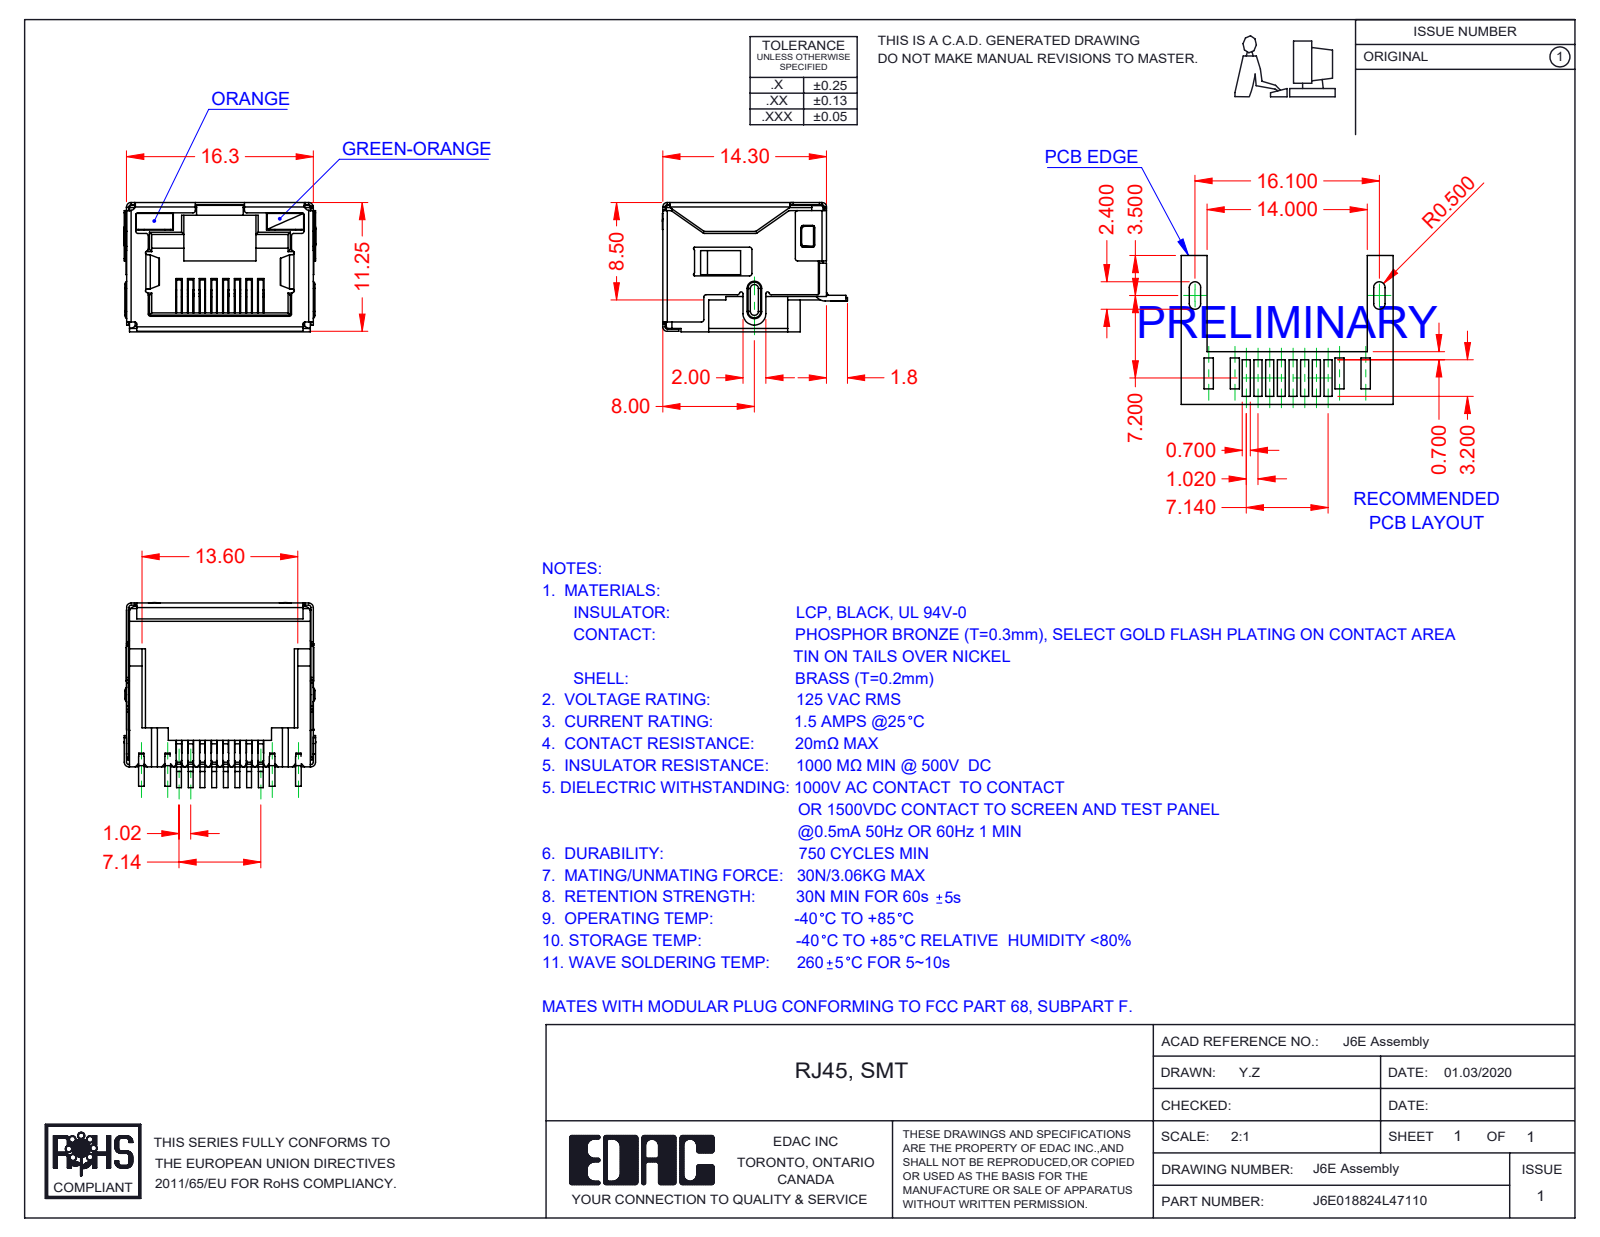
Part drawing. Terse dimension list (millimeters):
name: 6E LED LH_4-Orange; 6E LED RH_7-Green-Orange; 6E Insulator_LED; 6E Contacts (+2 more)
written by: SolidWorks 2016 (CONFIG_CONTROL_DESIGN)
unit: mm
bodies: 12 solids, 1498 faces (1099 planar, 349 cylindrical, 50 other)
size: 16.75 × 16.15 × 11.3
volume: 1 109 mm³; area: 4 045 mm²
rounds: 82× R0.2, 17× R0.25, 13× R0.4, 13× R0.5, 10× R0.1, 7× R0.15, 4× R0.3, 3× R1
face distances: 11.05, 16.05, 16.1, 15.85, 11.1, 11.3, 2.4, 0.7, 9.85, 0.49
